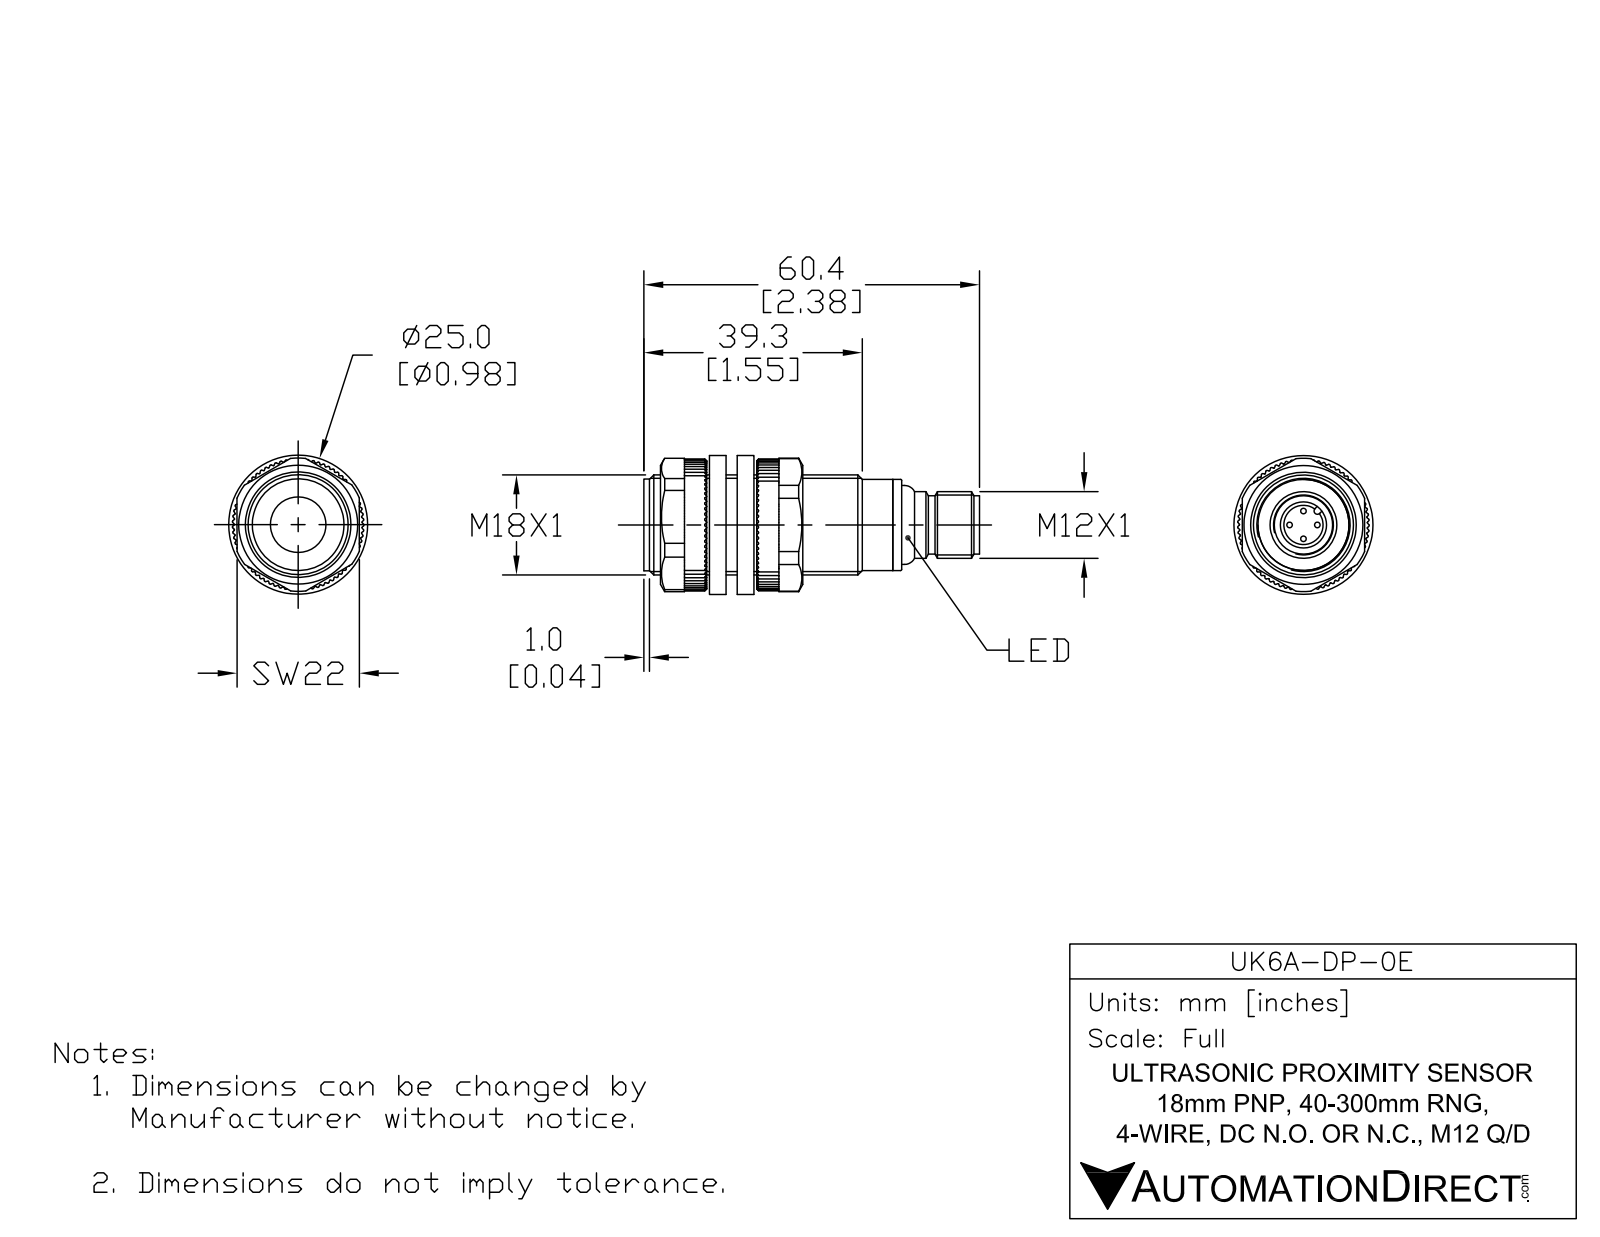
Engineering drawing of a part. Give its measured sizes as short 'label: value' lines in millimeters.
name: UK6A-DP-0E
written by: SolidWorks 2017 (AUTOMOTIVE_DESIGN)
unit: mm
bodies: 4 solids, 86 faces (15 planar, 36 cylindrical, 35 other)
size: 60.3 × 18 × 18
volume: 12 400 mm³; area: 4 934 mm²
holes: 1× ⌀7, 1× ⌀8.3, 1× ⌀9.5
bosses: 4× ⌀1, 1× ⌀18, 1× ⌀16.4, 1× ⌀15.8, 1× ⌀14.2, 1× ⌀12, 1× ⌀10.5
rounds: 1× R0.6
face distances: 43.8, 1, 44.8, 1, 44.8, 46.3, 46.3, 45.3, 1.5, 51.4
